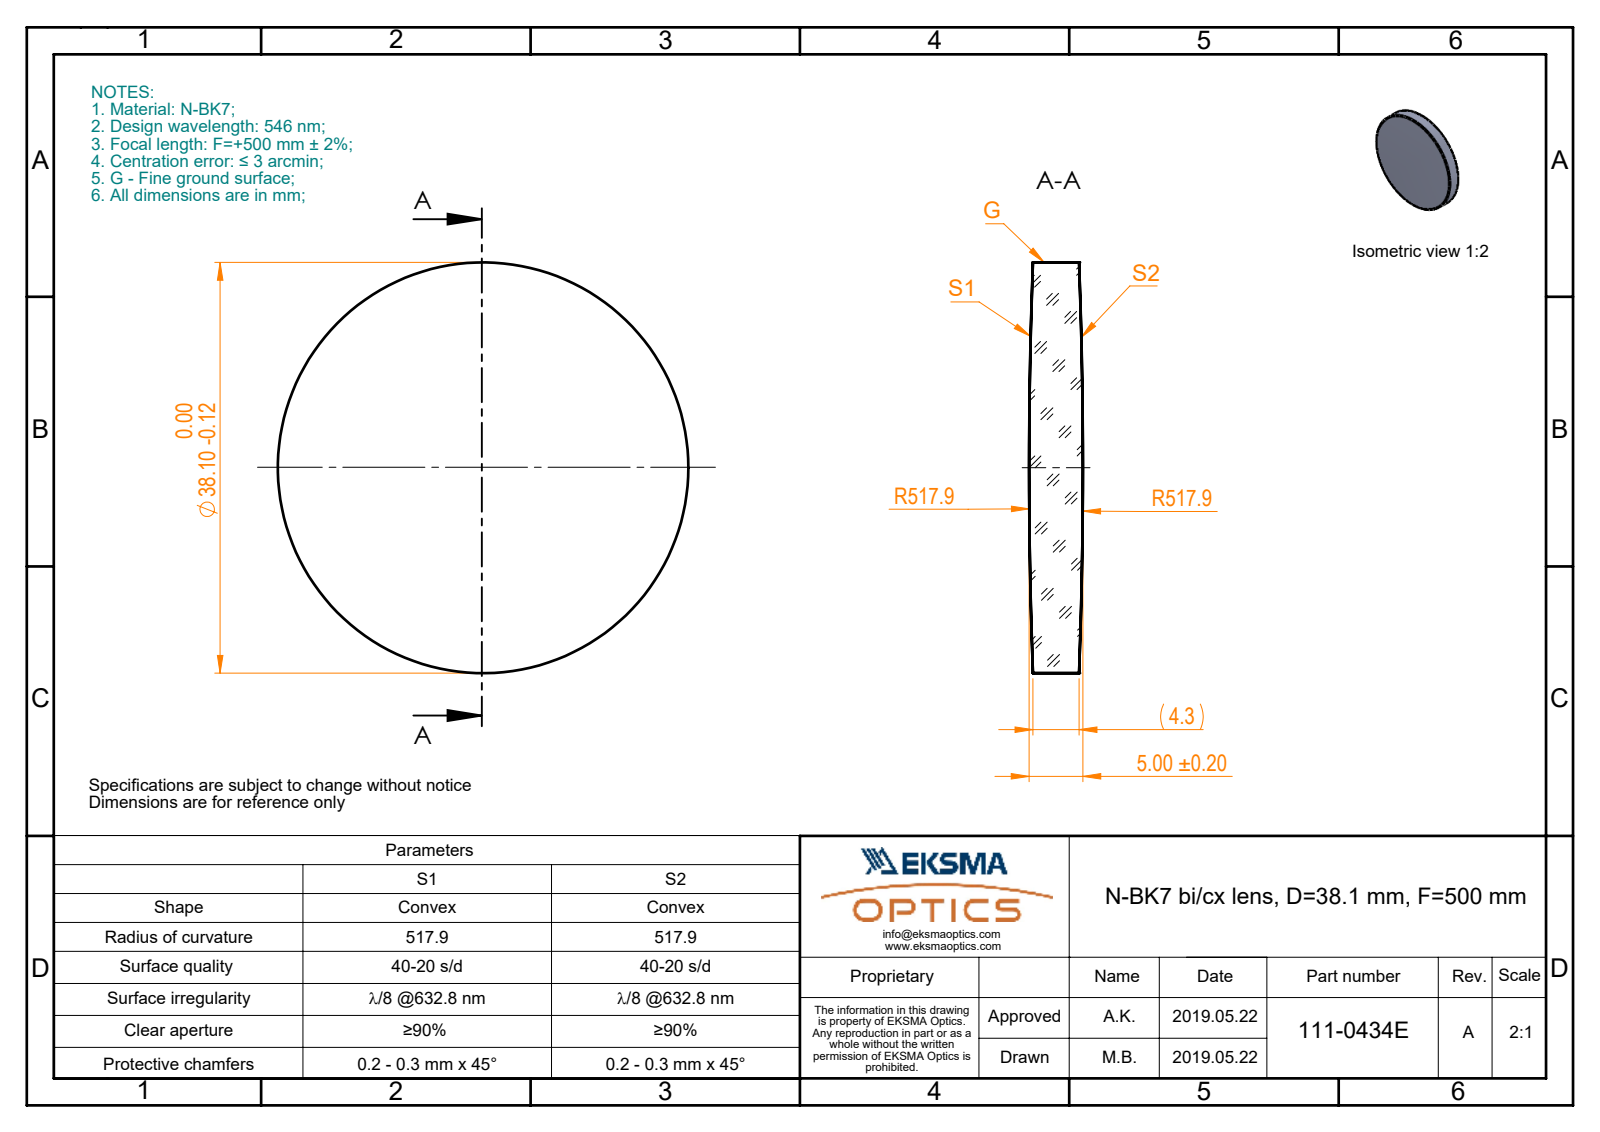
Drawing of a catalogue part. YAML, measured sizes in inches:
part_name: "111-0434E BK7 bi-cx 38.1 F500"
step_written_by: "SolidWorks 2017 (CONFIG_CONTROL_DESIGN)"
units: inches
bodies: {solids: 1, faces: 6, planar: 0, cylindrical: 2, other: 4}
overall_size: [1.5, 1.5, 0.197]
volume: 0.323
surface_area: 4.334
round_bosses_or_shafts:
  - {diameter: 1.5, count: 1}
